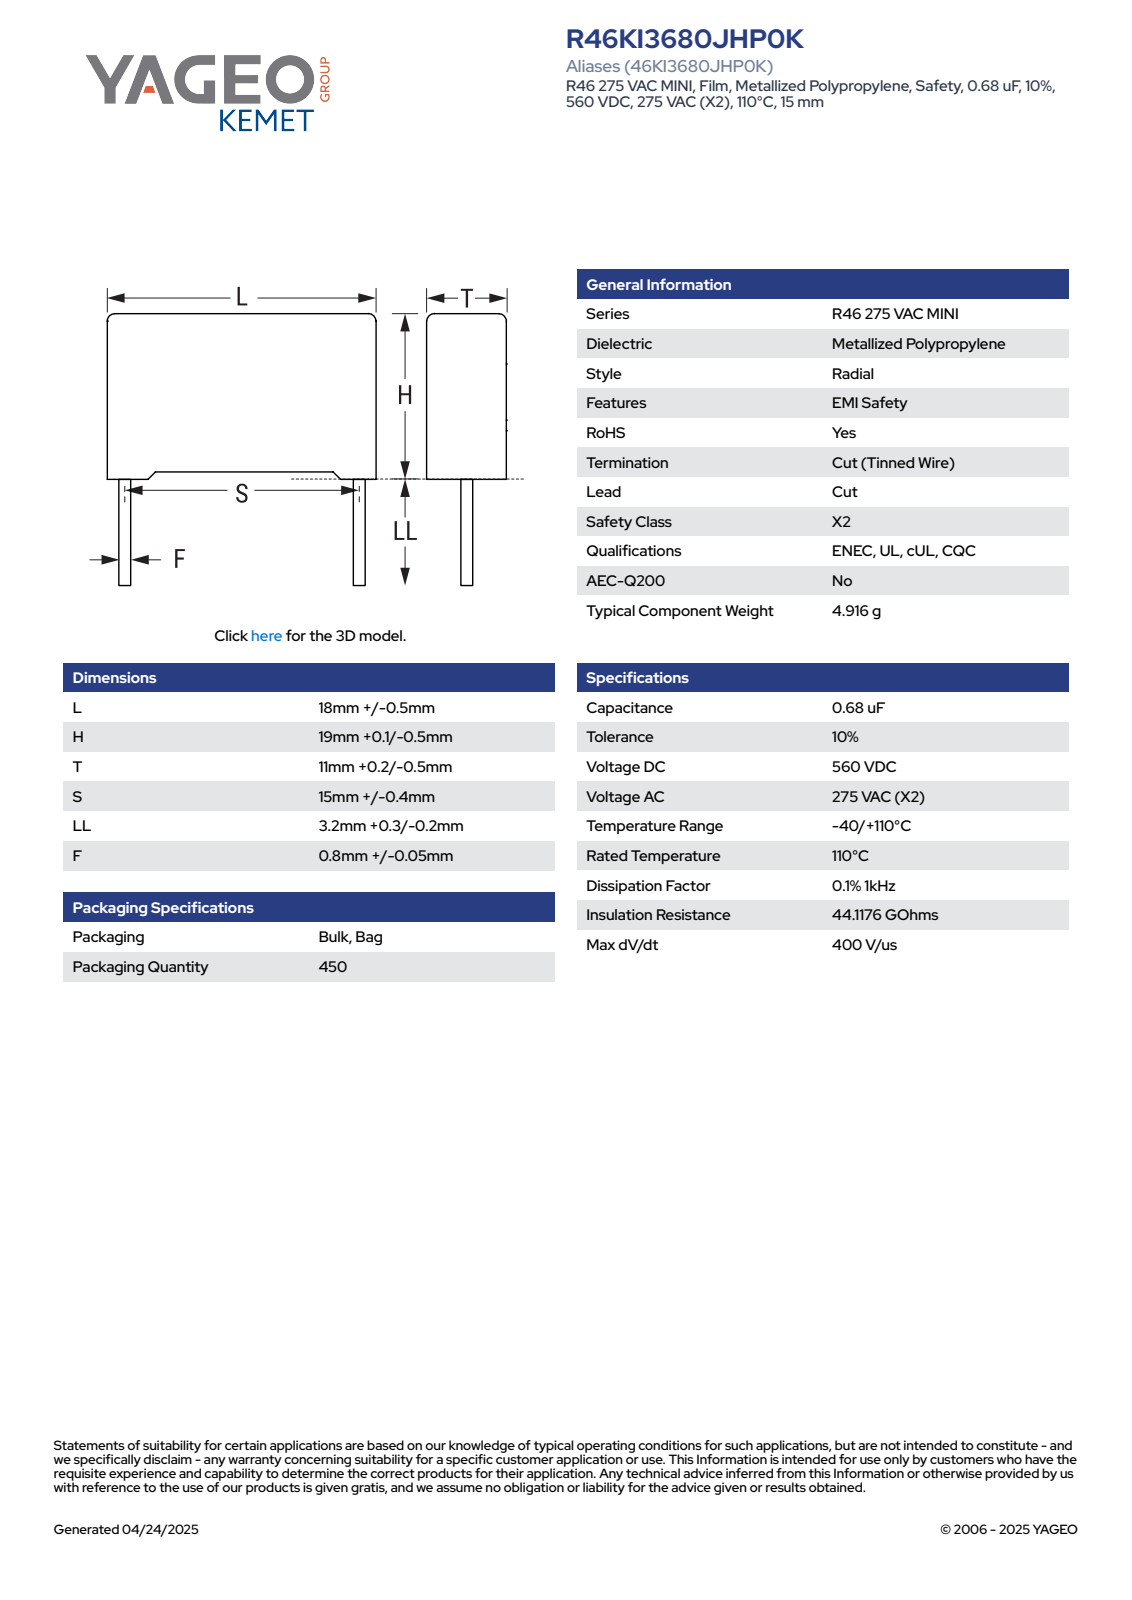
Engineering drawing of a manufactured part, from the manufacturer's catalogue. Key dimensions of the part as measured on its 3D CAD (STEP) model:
Part name (STEP PRODUCT): CFR_RB2_18X19X11_L18.5H19.1T11.2S15LL3.5F0.85
STEP written by: SolidWorks 2021 (AUTOMOTIVE_DESIGN)
Units: millimetres
Bodies: 4 solids, 85 faces (77 planar, 8 cylindrical, 0 other)
Overall size (bounding box): 22.6 × 18.5 × 11.21
Volume: 3 821 mm³ · Surface area: 1 596 mm²
Round bosses / shafts (diameter × count): ⌀0.85 ×2
Partial cylindrical surfaces — rounded edges, fillets, slot ends (radius × count): R0.5 ×4
Main face-to-face distances: 11.2, 18.5, 18.35, 0.62, 0.75, 19.1, 17.88, 0.66, 18.44, 10.58
